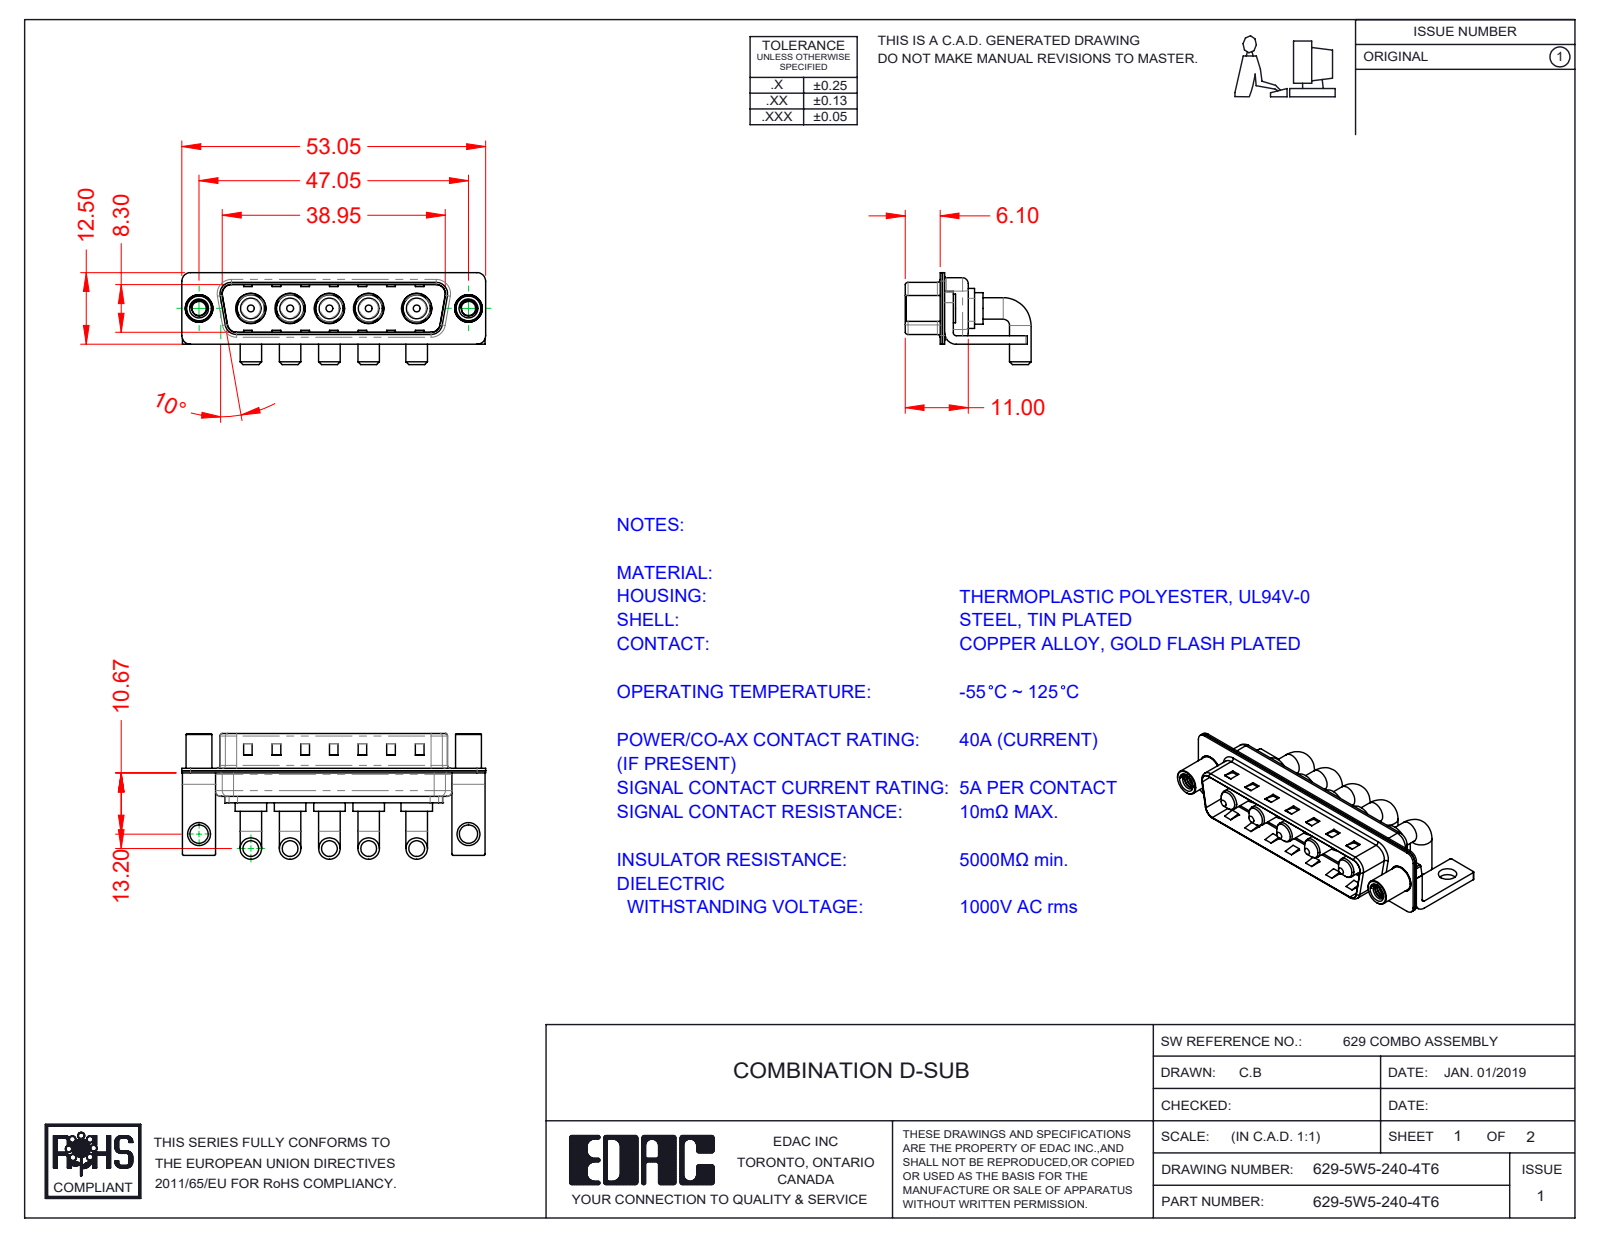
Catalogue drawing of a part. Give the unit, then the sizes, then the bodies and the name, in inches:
Units: inches
Overall size (bounding box): 2.089 × 0.865 × 0.632
Round holes (diameter × count): ⌀0.191 ×5, ⌀0.209 ×5, ⌀0.098 ×2, ⌀0.126 ×2, ⌀0.157 ×2, ⌀0.189 ×2
Round bosses / shafts (diameter × count): ⌀0.148 ×10, ⌀0.217 ×5, ⌀0.205 ×5, ⌀0.187 ×5, ⌀0.142 ×5, ⌀0.197 ×2, ⌀0.193 ×2, ⌀0.177 ×2
Partial cylindrical surfaces — rounded edges, fillets, slot ends (radius × count): R0.01 ×16, R0.059 ×16, R0.079 ×13, R0.02 ×9, R0.063 ×8, R0.083 ×5, R0.024 ×4, R0.026 ×4
Main face-to-face distances: 0.016, 0.031, 0.374, 0.059, 0.358, 0.343, 0.39, 0.205, 0.03, 0.047
Hole centre spacings: 0.27, 0.541, 1.852, 0.27, 0.27, 0.33, 0.33, 0.356
Volume: 0.253 in³ · Surface area: 12.85 in²
Bodies: 17 solids, 689 faces (243 planar, 314 cylindrical, 132 other)
Part name (STEP PRODUCT): 629Combo Stabilizer Bracket; 629Combo Housing_5W5; 629-5W5-240-4T6; Power Pin_40A RA (+3 more)
STEP written by: SolidWorks 2020 (CONFIG_CONTROL_DESIGN)
